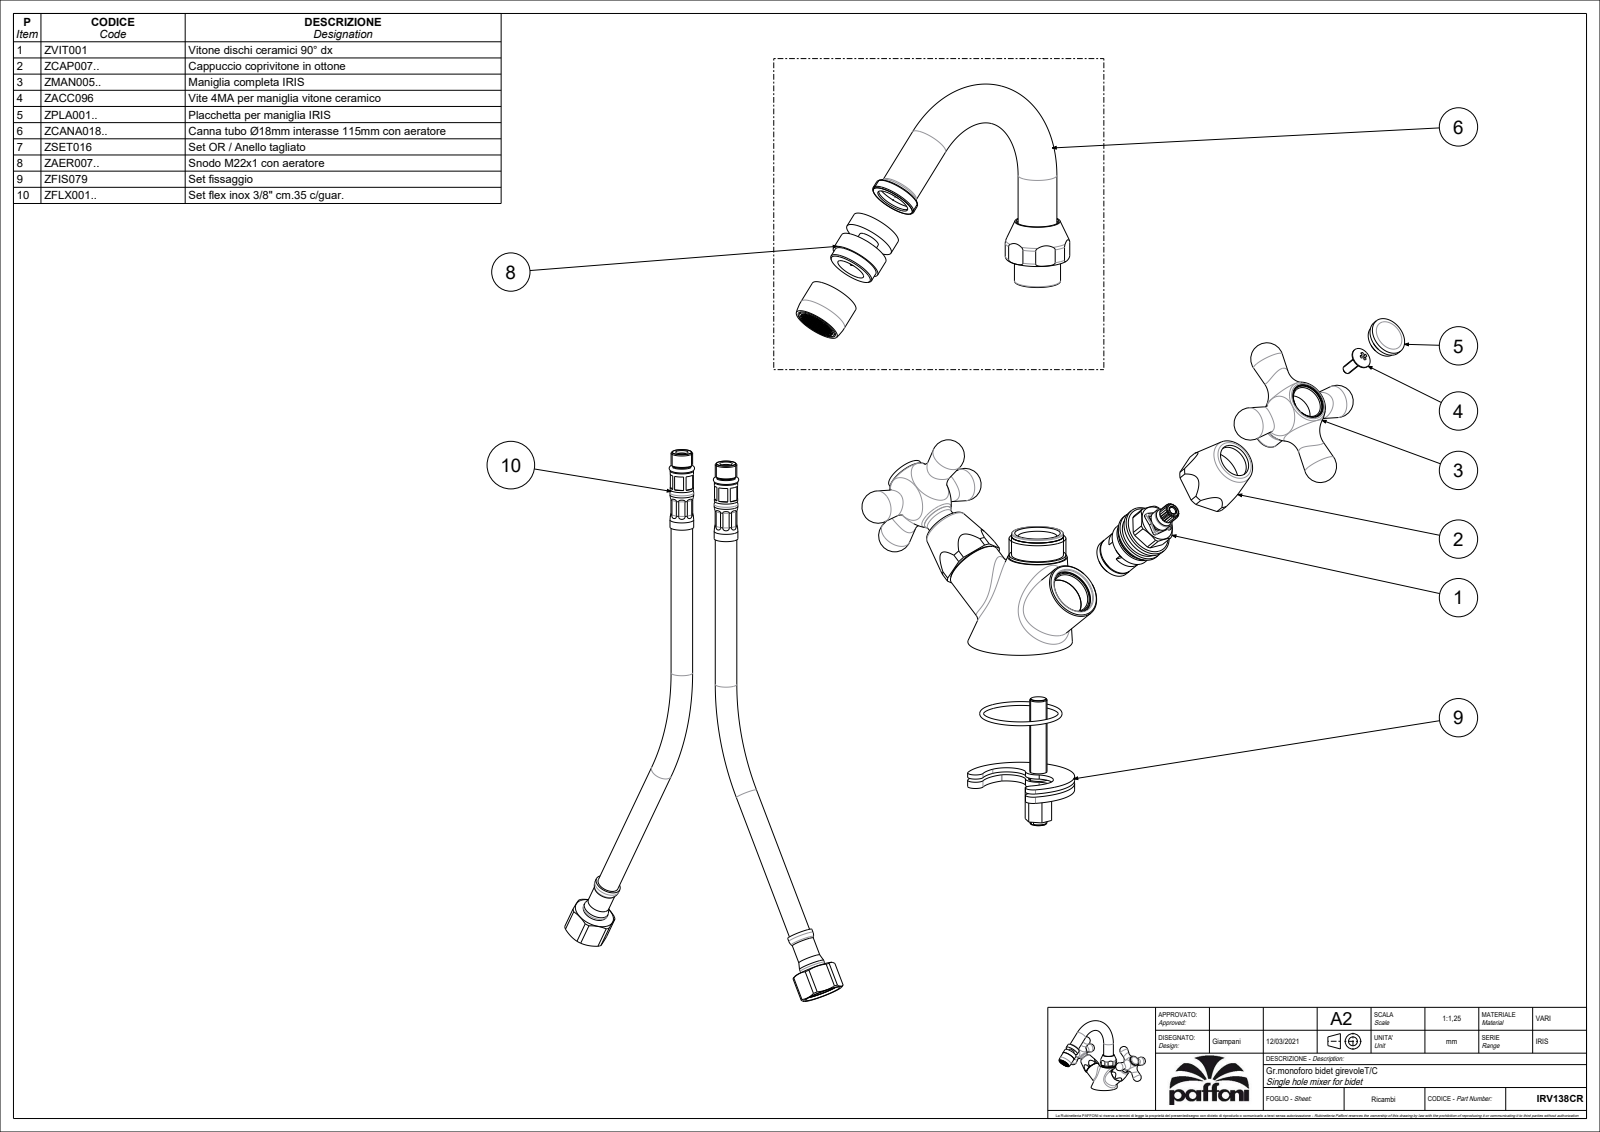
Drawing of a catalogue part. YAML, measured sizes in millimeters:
part_name: "IRV138CR"
step_written_by: "CREO PARAMETRIC BY PTC INC, 2020044 (CONFIG_CONTROL_DESIGN)"
units: millimeters
bodies: {solids: 1, faces: 463, planar: 139, cylindrical: 108, other: 216}
overall_size: [183.98, 151.19, 132.5]
volume: 165196
surface_area: 52216
round_holes:
  - {diameter: 9, count: 4}
  - {diameter: 8, count: 2}
  - {diameter: 11, count: 2}
  - {diameter: 15.7, count: 2}
  - {diameter: 18, count: 2}
  - {diameter: 19, count: 2}
  - {diameter: 21, count: 2}
  - {diameter: 21.5, count: 2}
  - {diameter: 23, count: 2}
  - {diameter: 6, count: 1}
  - {diameter: 6.8, count: 1}
  - {diameter: 12.6, count: 1}
round_bosses_or_shafts:
  - {diameter: 18, count: 4}
  - {diameter: 26.3, count: 2}
  - {diameter: 13.5, count: 2}
  - {diameter: 34, count: 1}
  - {diameter: 26.4, count: 1}
  - {diameter: 24, count: 1}
  - {diameter: 23.6, count: 1}
  - {diameter: 18.8, count: 1}
partial_cylinders:
  - {radius: 14.5, count: 2}
  - {radius: 15, count: 1}
face_to_face_distances: [26.49, 22, 5, 28.5, 24.01, 23.7, 28.7, 1.3, 46.01, 41.7]
hole_center_spacings: [7, 13.38, 13.89, 0.6, 11.4, 12, 14]
